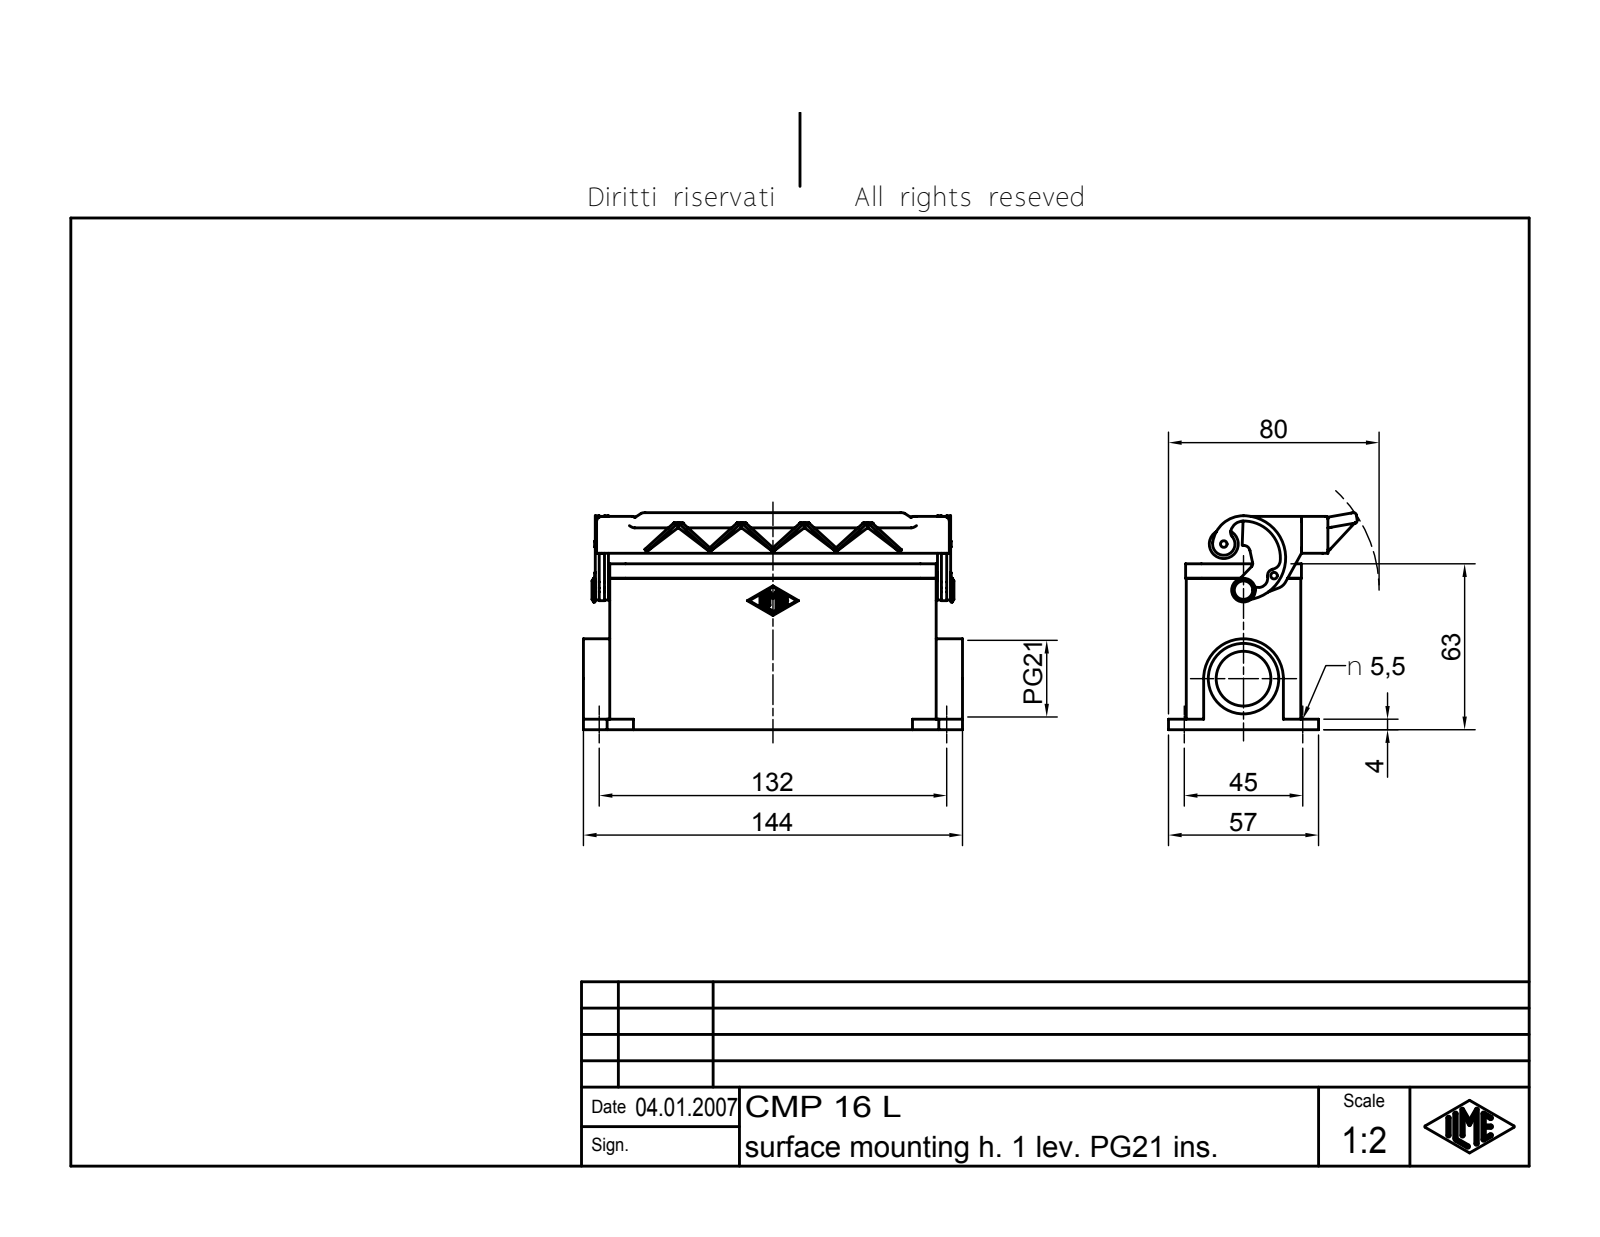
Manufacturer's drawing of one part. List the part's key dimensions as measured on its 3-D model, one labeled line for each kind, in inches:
Part name (STEP PRODUCT): CMP 16 L
STEP written by: Autodesk Inventor 7 (AUTOMOTIVE_DESIGN)
Units: inches
Bodies: 4 solids, 463 faces (191 planar, 123 cylindrical, 149 other)
Overall size (bounding box): 5.669 × 3.245 × 2.823
Volume: 7.782 in³ · Surface area: 112.5 in²
Round holes (diameter × count): ⌀0.217 ×4, ⌀0.079 ×1, ⌀0.818 ×1, ⌀1.054 ×1
Round bosses / shafts (diameter × count): ⌀0.433 ×1, ⌀0.354 ×1, ⌀0.197 ×1, ⌀0.118 ×1, ⌀0.098 ×1
Partial cylindrical surfaces — rounded edges, fillets, slot ends (radius × count): R0.015 ×14, R0.079 ×12, R0.236 ×8, R0.039 ×7, R0.059 ×5, R0.118 ×4, R0.098 ×3, R0.138 ×2
Main face-to-face distances: 0.118, 1.594, 0.157, 1.713, 1.476, 0.128, 0.03, 2.264, 2.106, 0.413
Hole centre spacings: 1.772, 5.197, 5.491, 1.606
